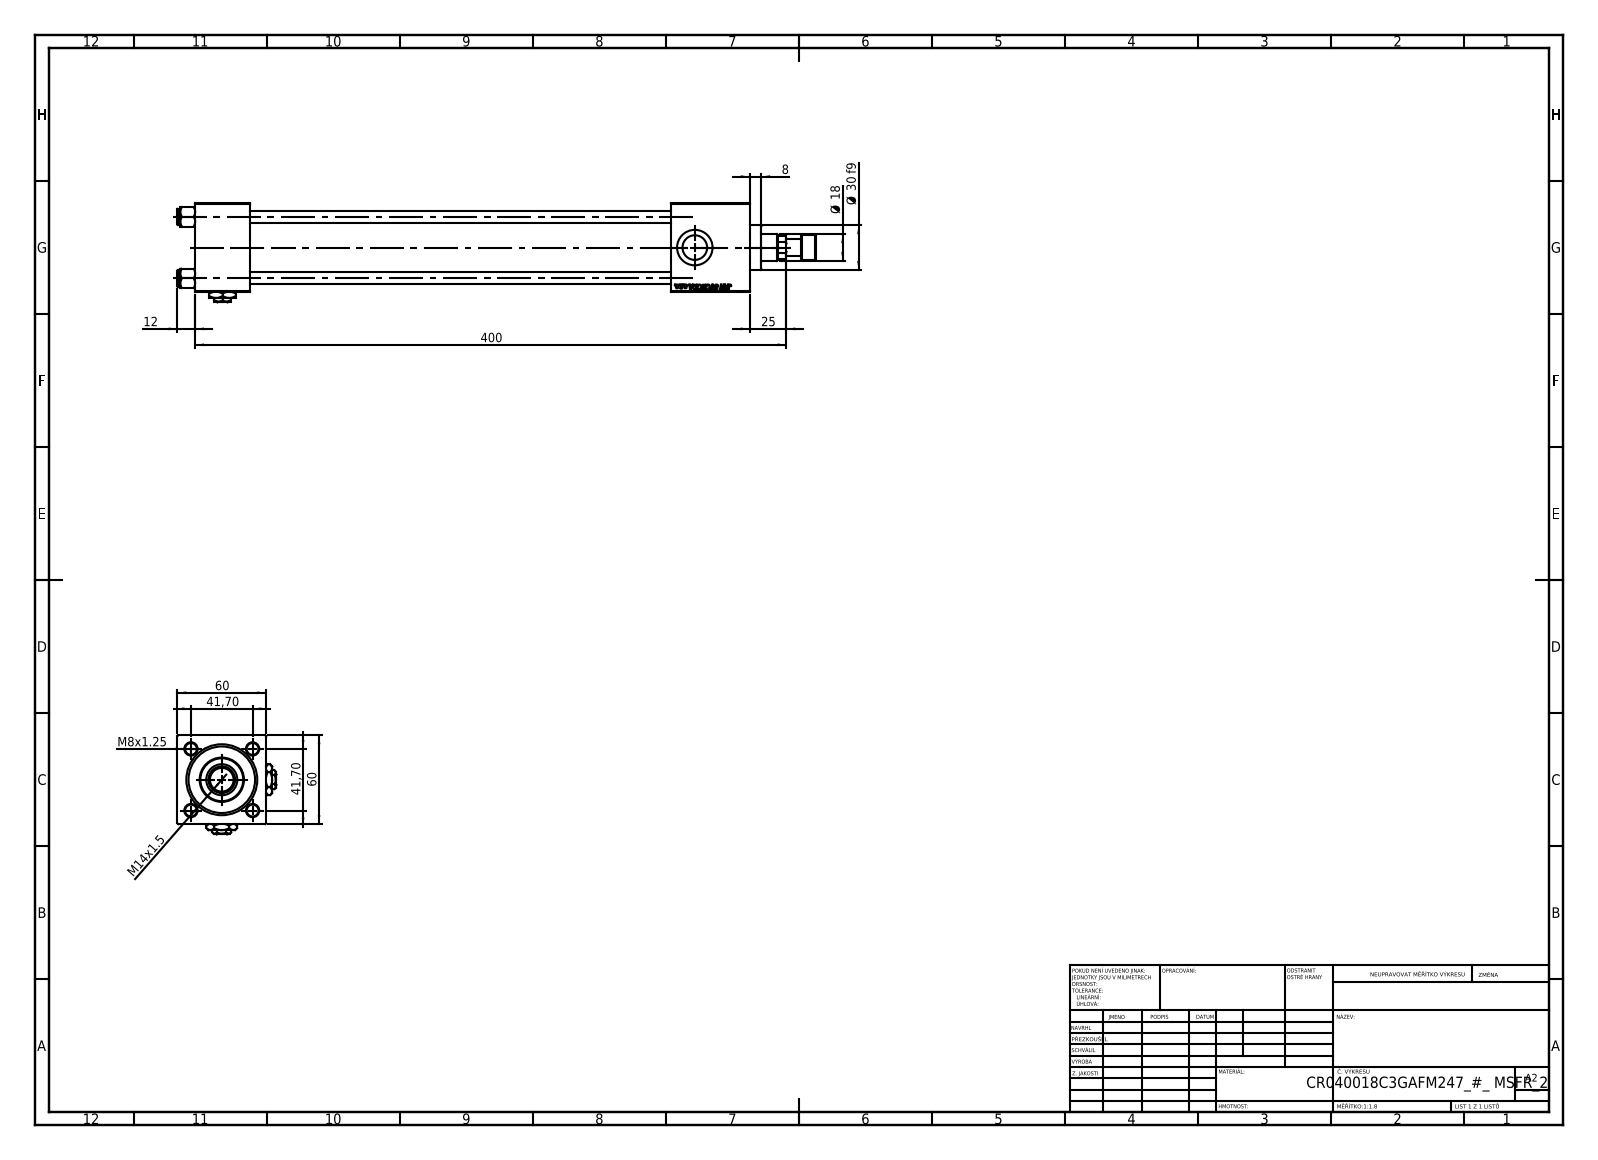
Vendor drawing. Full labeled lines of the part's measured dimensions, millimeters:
Part name (STEP PRODUCT): V215_VC_A; V215CR_VCP_C; V215CR_C_TYCINKA; V215CR_C_Body (+3 more)
STEP written by: SolidWorks 2019 (CONFIG_CONTROL_DESIGN)
Units: millimetres
Bodies: 14 solids, 1261 faces (577 planar, 102 cylindrical, 582 other)
Overall size (bounding box): 432 × 67 × 67
Volume: 597 457 mm³ · Surface area: 206 633 mm²
Round holes (diameter × count): ⌀8 ×4, ⌀7 ×2, ⌀16.66 ×2, ⌀24 ×2, ⌀8.5 ×1, ⌀18 ×1, ⌀21 ×1, ⌀31 ×1, ⌀40 ×1, ⌀45 ×1
Round bosses / shafts (diameter × count): ⌀11 ×5, ⌀46 ×1, ⌀30 ×1, ⌀17 ×1
Main face-to-face distances: 60, 37, 375, 338, 53, 322, 285, 346.3, 309.3, 24.3
Hole centre spacings: 29.49, 41.7, 58.97
